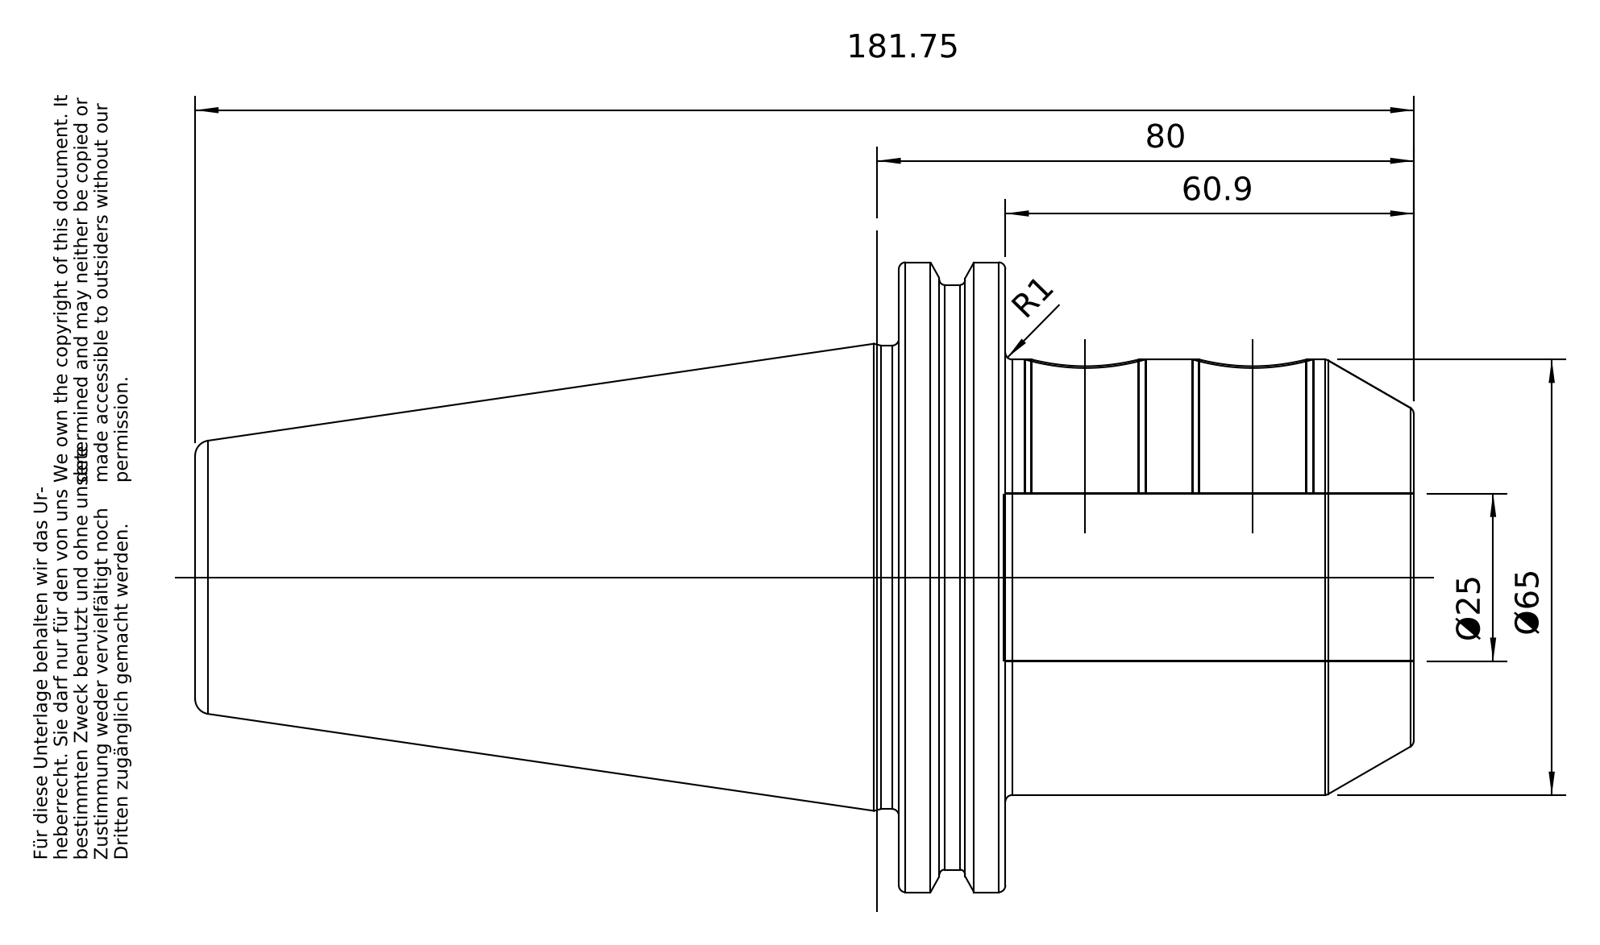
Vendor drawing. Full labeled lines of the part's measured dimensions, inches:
Part name (STEP PRODUCT): 50-300-25
STEP written by: PRO/ENGINEER BY PARAMETRIC TECHNOLOGY CORPORATION, 2010430 (CONFIG_CONTROL_DESIGN)
Units: inches
Bodies: 1 solid, 107 faces (21 planar, 36 cylindrical, 50 other)
Overall size (bounding box): 7.15 × 3.837 × 3.701
Volume: 30.16 in³ · Surface area: 96.26 in²
Round holes (diameter × count): ⌀0.63 ×2, ⌀0.709 ×2, ⌀0.817 ×1, ⌀0.984 ×1, ⌀0.985 ×1, ⌀1.012 ×1
Round bosses / shafts (diameter × count): ⌀3.583 ×1, ⌀2.722 ×1, ⌀2.559 ×1, ⌀0.945 ×1
Partial cylindrical surfaces — rounded edges, fillets, slot ends (radius × count): R0.069 ×5, R1.919 ×1
Main face-to-face distances: 0.624, 3.024, 2.4, 0.618, 2.406, 4.126, 4.744, 4.75, 7.15, 2.866
Hole centre spacings: 0.984
